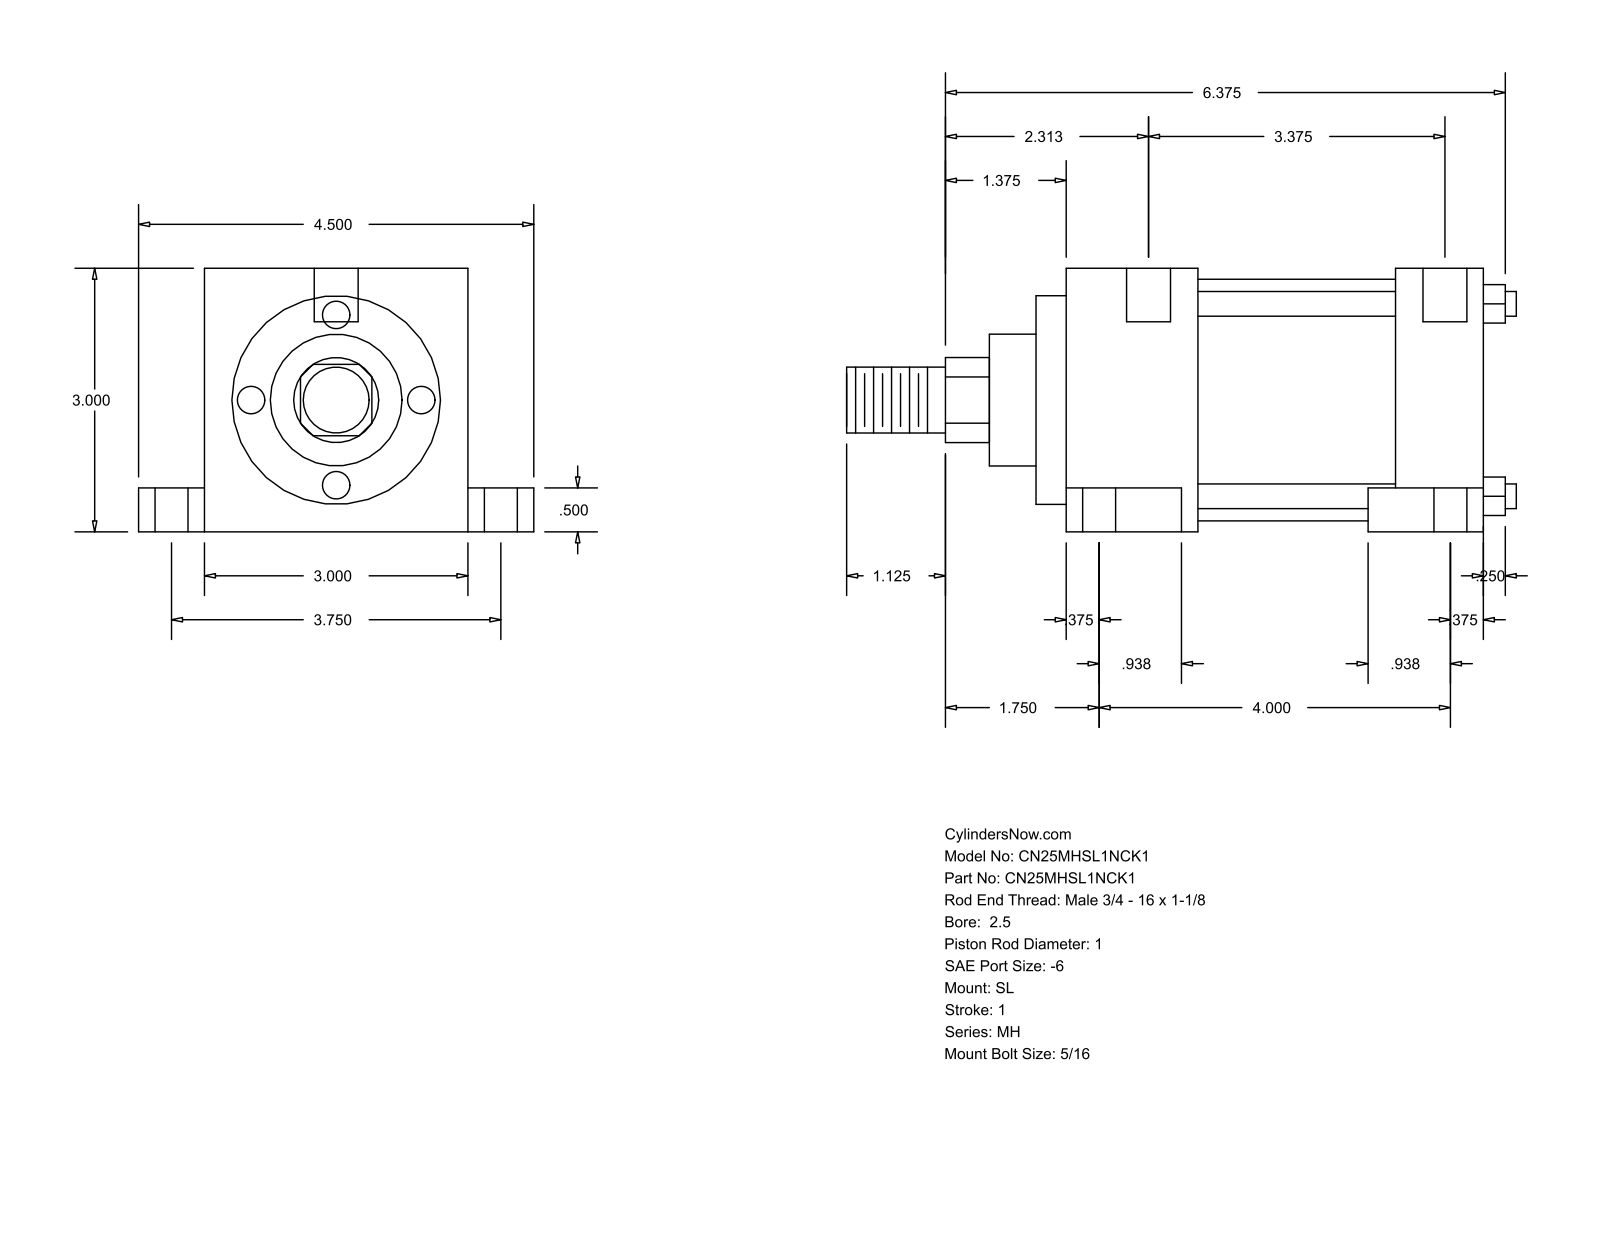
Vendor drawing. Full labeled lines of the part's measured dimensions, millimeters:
Part name (STEP PRODUCT): MH_SL__0250_1
STEP written by: GSSL Pune (CONFIG_CONTROL_DESIGN)
Units: millimetres
Bodies: 0 solids, 86 faces (61 planar, 25 cylindrical, 0 other)
Overall size (bounding box): 193.68 × 114.3 × 76.2
Round holes (diameter × count): ⌀5.56 ×2, ⌀9.53 ×2, ⌀15.88 ×2, ⌀12.7 ×1
Round bosses / shafts (diameter × count): ⌀7.14 ×4, ⌀69.85 ×1, ⌀60.33 ×1, ⌀38.1 ×1, ⌀25.4 ×1, ⌀19.05 ×1
Partial cylindrical surfaces — rounded edges, fillets, slot ends (radius × count): R12.29 ×1
Main face-to-face distances: 76.2, 25.39, 103.99, 129.38, 12.7, 63.5, 19.05, 95.25, 13.49, 117.48
Hole centre spacings: 47.65, 3.18, 95.24
